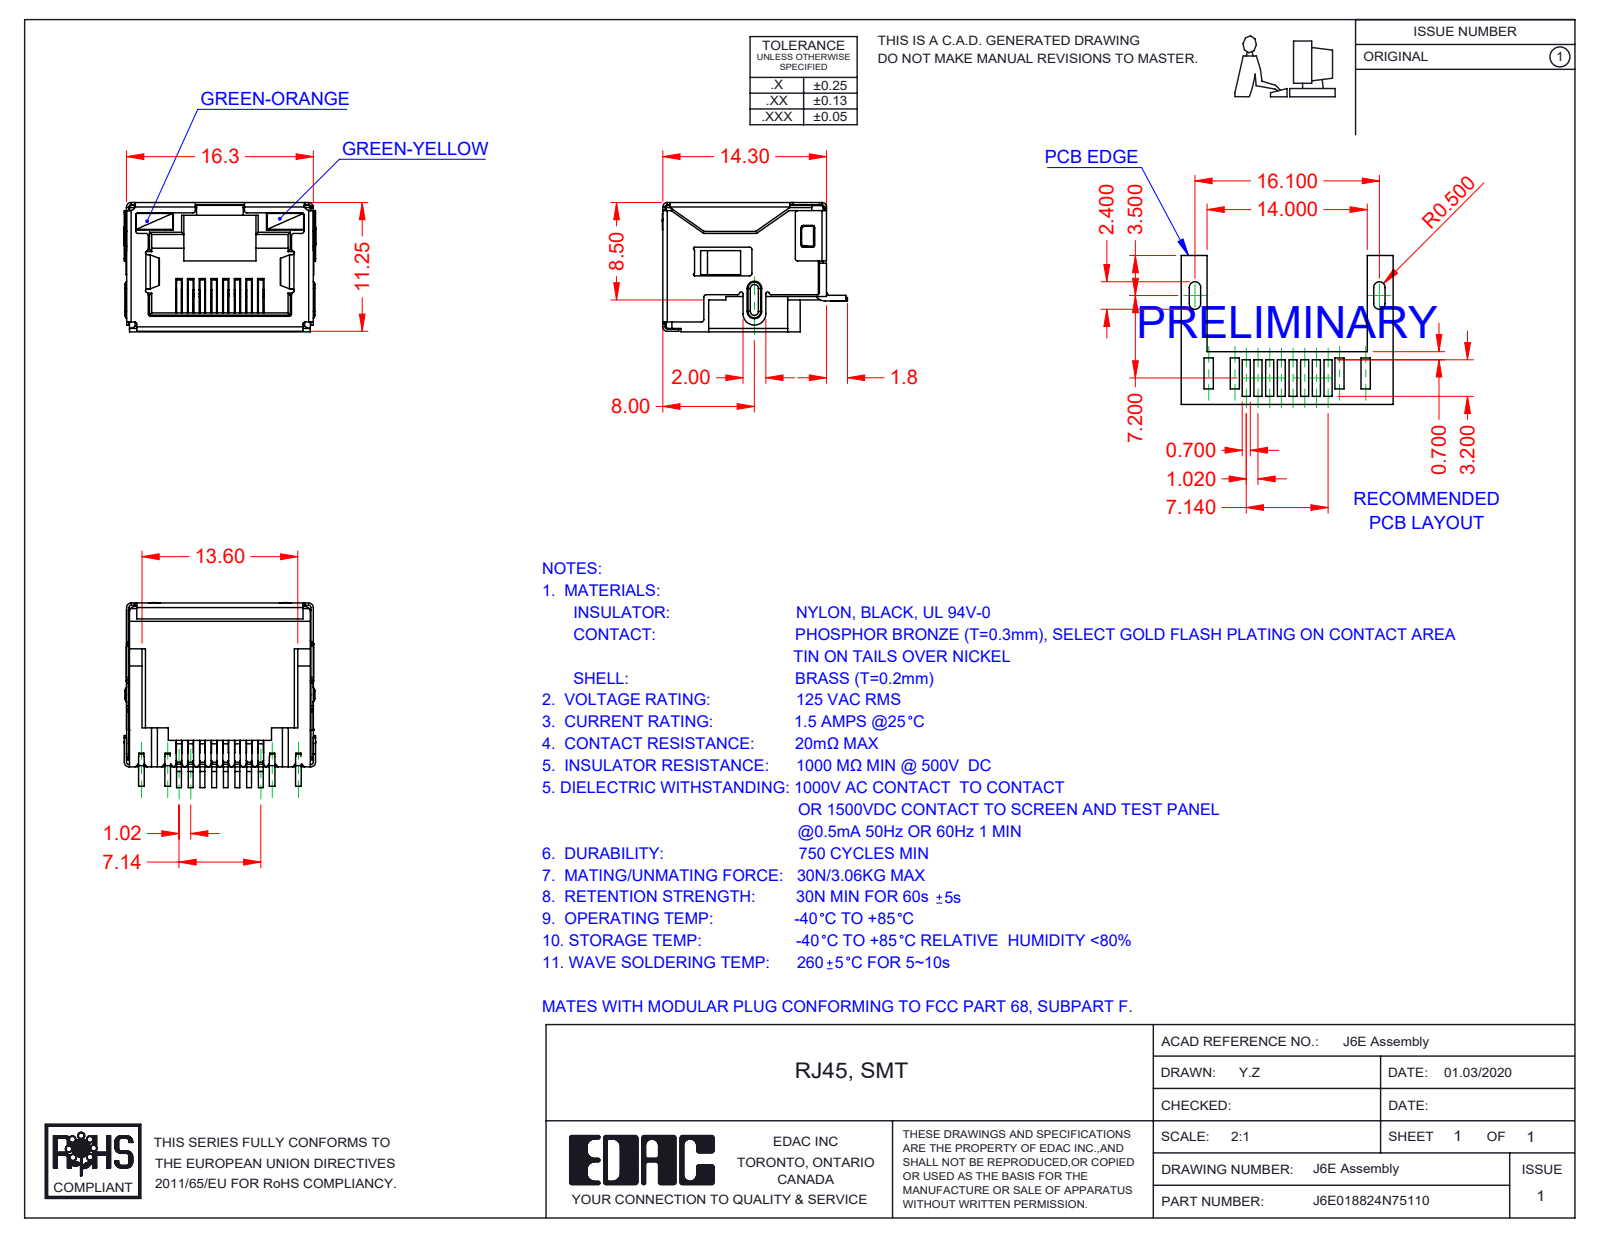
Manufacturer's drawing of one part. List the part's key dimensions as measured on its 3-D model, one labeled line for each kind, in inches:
Part name (STEP PRODUCT): 6E Insulator_LED; J6E018824N75110; 6E LED RH_5-Green-Yellow; 6E Contacts (+2 more)
STEP written by: SolidWorks 2016 (CONFIG_CONTROL_DESIGN)
Units: inches
Bodies: 12 solids, 1500 faces (1099 planar, 351 cylindrical, 50 other)
Overall size (bounding box): 0.659 × 0.636 × 0.445
Volume: 0.068 in³ · Surface area: 6.27 in²
Partial cylindrical surfaces — rounded edges, fillets, slot ends (radius × count): R0.008 ×82, R0.01 ×17, R0.016 ×13, R0.02 ×13, R0.004 ×10, R0.006 ×7, R0.012 ×4, R0.039 ×3
Main face-to-face distances: 0.435, 0.632, 0.634, 0.624, 0.437, 0.445, 0.094, 0.028, 0.388, 0.019
